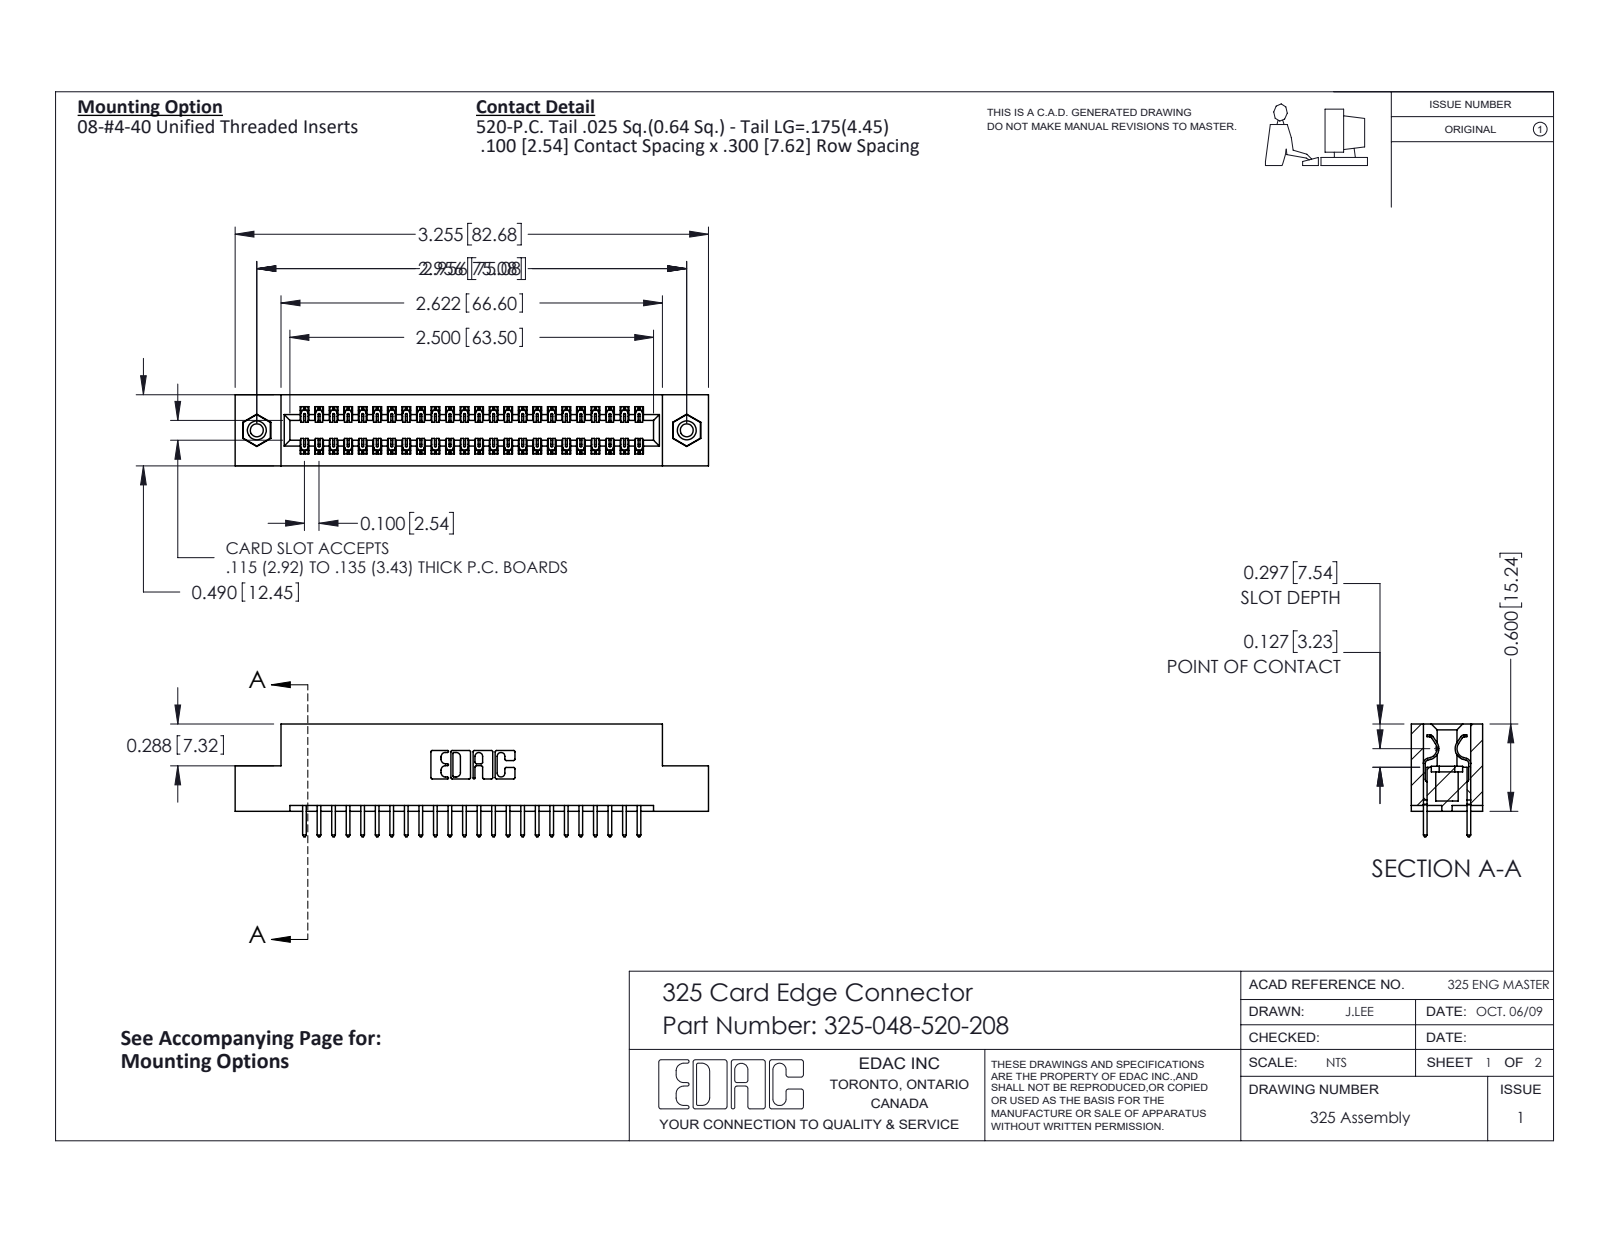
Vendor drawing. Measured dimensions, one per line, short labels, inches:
name: 325 Part_TI; 345-250-001_345-250-003-102; 325-048-520-208; 325-292-001_325-293-120
written by: SolidWorks 2016 (CONFIG_CONTROL_DESIGN)
unit: in
bodies: 51 solids, 2670 faces (1830 planar, 824 cylindrical, 16 other)
size: 3.255 × 0.775 × 0.49
volume: 0.641 in³; area: 18.9 in²
holes: 2× ⌀0.089, 2× ⌀0.125, 2× ⌀0.16
bosses: 2× ⌀0.155
rounds: 72× R0.006, 48× R0.01, 22× R0.01, 6× R0.007, 6× R0.031, 3× R0.026, 2× R0.014, 2× R0.022
face distances: 0.083, 0.407, 0.3, 0.49, 0.107, 0.383, 0.025, 0.325, 0.04, 0.6
hole spacings: 2.956
